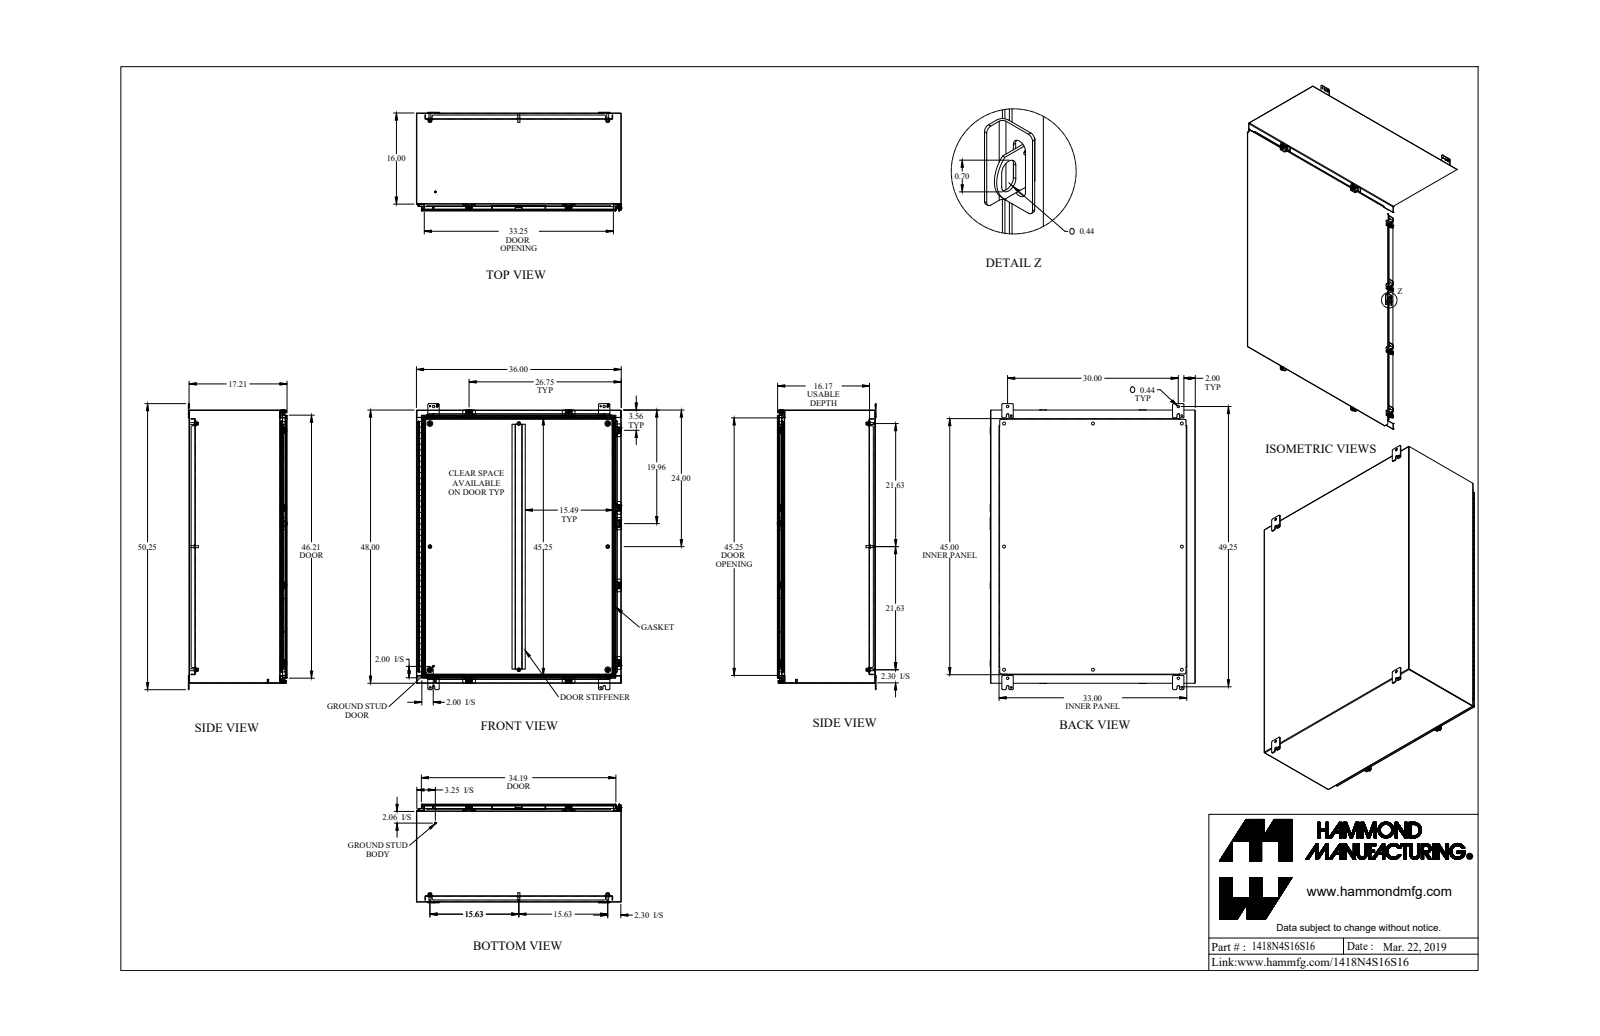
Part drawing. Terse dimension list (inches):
name: 1418N4S16S16_Default
written by: SolidWorks 2019 (CONFIG_CONTROL_DESIGN)
unit: in
bodies: 66 solids, 2103 faces (1108 planar, 853 cylindrical, 142 other)
size: 50.25 × 36.063 × 17.375
volume: 656.8 in³; area: 17 248 in²
holes: 8× ⌀0.213, 8× ⌀0.265, 8× ⌀0.375, 8× ⌀0.5, 4× ⌀0.307, 4× ⌀0.313, 4× ⌀0.437, 4× ⌀0.445, 1× ⌀0.11, 1× ⌀0.125
bosses: 8× ⌀0.65, 8× ⌀0.5, 8× ⌀0.39, 8× ⌀0.375, 8× ⌀0.332, 8× ⌀0.244, 4× ⌀1, 2× ⌀0.313
rounds: 44× R0.25, 39× R0.048, 39× R0.143, 30× R0.188, 22× R0.036, 22× R0.108, 16× R0.141, 14× R0.125
face distances: 0.072, 17.066, 17.138, 0.072, 0.095, 17.138, 17.21, 0.937, 35.928, 1.009
hole spacings: 38.003, 51.507, 7.196, 15.625, 21.625, 24.468, 45.893, 45.986
